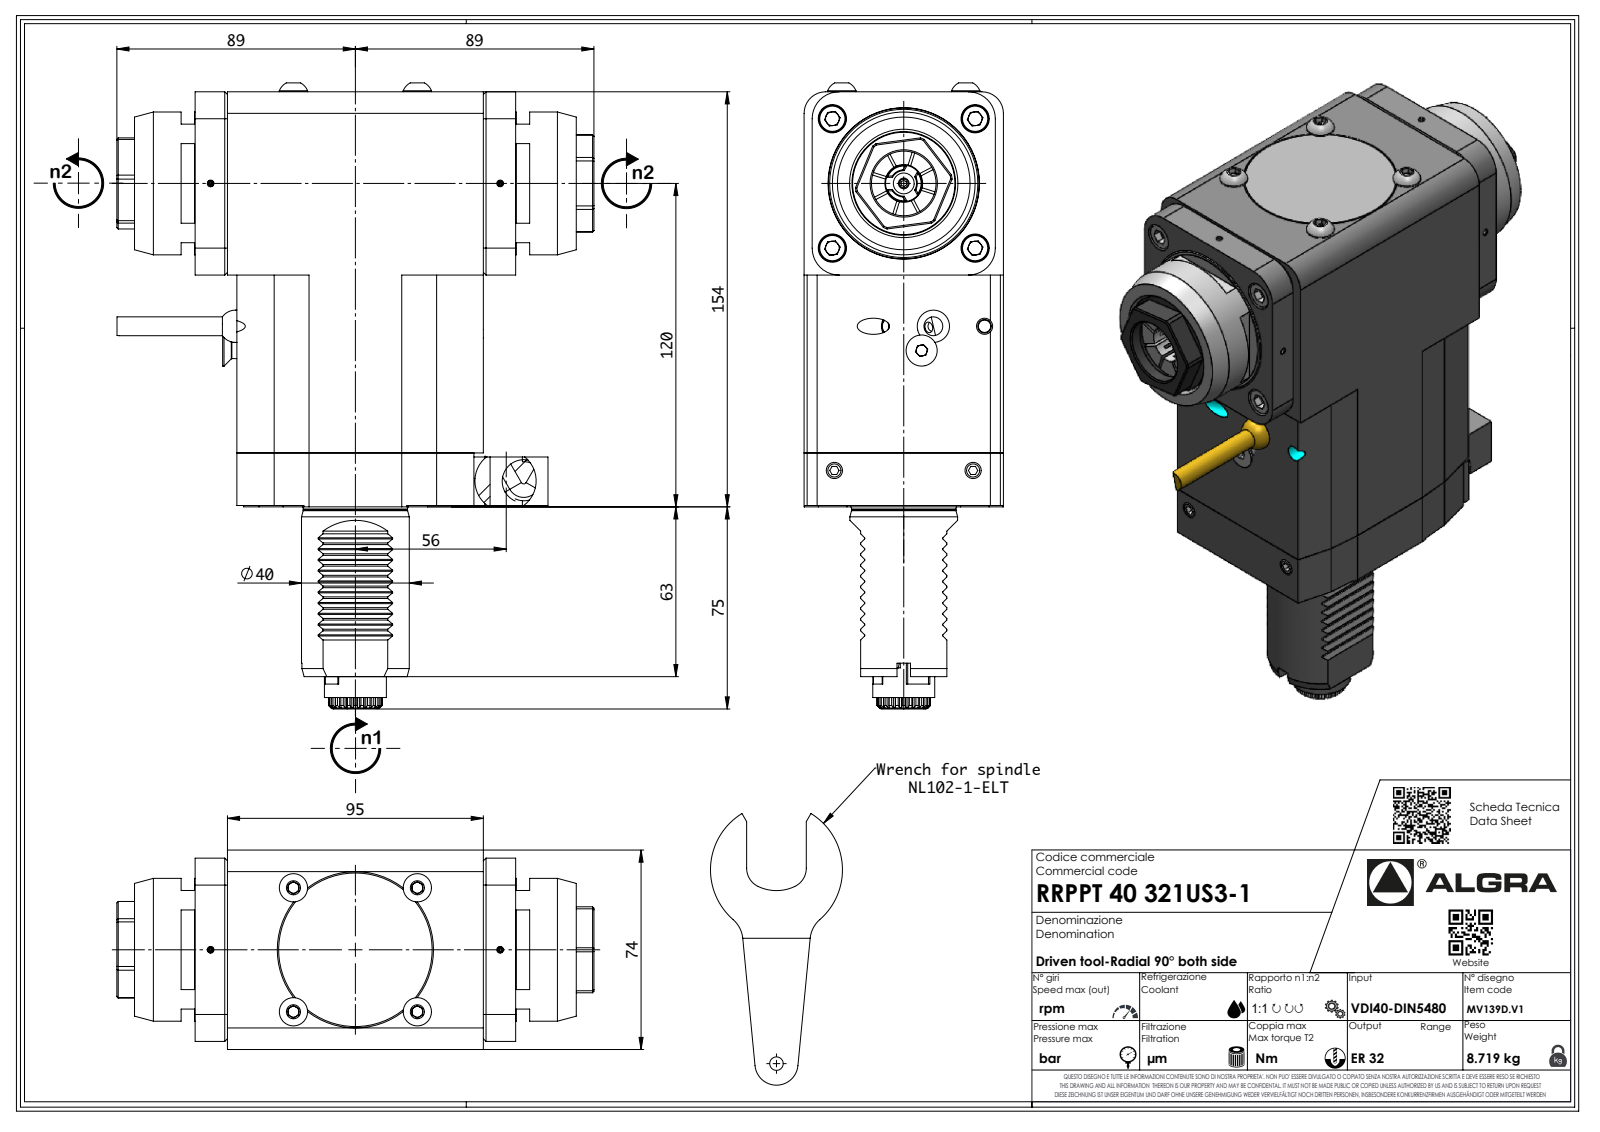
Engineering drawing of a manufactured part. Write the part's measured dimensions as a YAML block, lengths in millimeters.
part_name: "RRPPT40321US3-1"
step_written_by: "SolidWorks 2023 (AUTOMOTIVE_DESIGN)"
units: millimeters
bodies: {solids: 3, faces: 1173, planar: 799, cylindrical: 185, other: 189}
overall_size: [232.3, 177.11, 74]
volume: 1331000
surface_area: 104856
round_holes:
  - {diameter: 5, count: 5}
  - {diameter: 6.2, count: 5}
  - {diameter: 2.5, count: 4}
  - {diameter: 7, count: 4}
  - {diameter: 10.5, count: 4}
  - {diameter: 4, count: 2}
  - {diameter: 6, count: 2}
  - {diameter: 2.1, count: 1}
  - {diameter: 24, count: 1}
  - {diameter: 30.4, count: 1}
  - {diameter: 31, count: 1}
  - {diameter: 53, count: 1}
round_bosses_or_shafts:
  - {diameter: 10.5, count: 6}
  - {diameter: 6, count: 3}
  - {diameter: 53, count: 1}
  - {diameter: 40, count: 1}
  - {diameter: 38.7, count: 1}
  - {diameter: 28.26, count: 1}
  - {diameter: 23, count: 1}
  - {diameter: 11.57, count: 1}
partial_cylinders:
  - {radius: 0.3, count: 20}
  - {radius: 0.33, count: 7}
  - {radius: 0.52, count: 7}
  - {radius: 3.7, count: 7}
  - {radius: 10, count: 4}
  - {radius: 8, count: 2}
  - {radius: 0.21, count: 1}
  - {radius: 9.92, count: 1}
face_to_face_distances: [74, 154, 91.5, 12, 141.5, 22.5, 107, 119, 68, 84.92]
hole_center_spacings: [35.75, 8, 48, 51.5, 52.12, 53, 53.75, 71.51]
